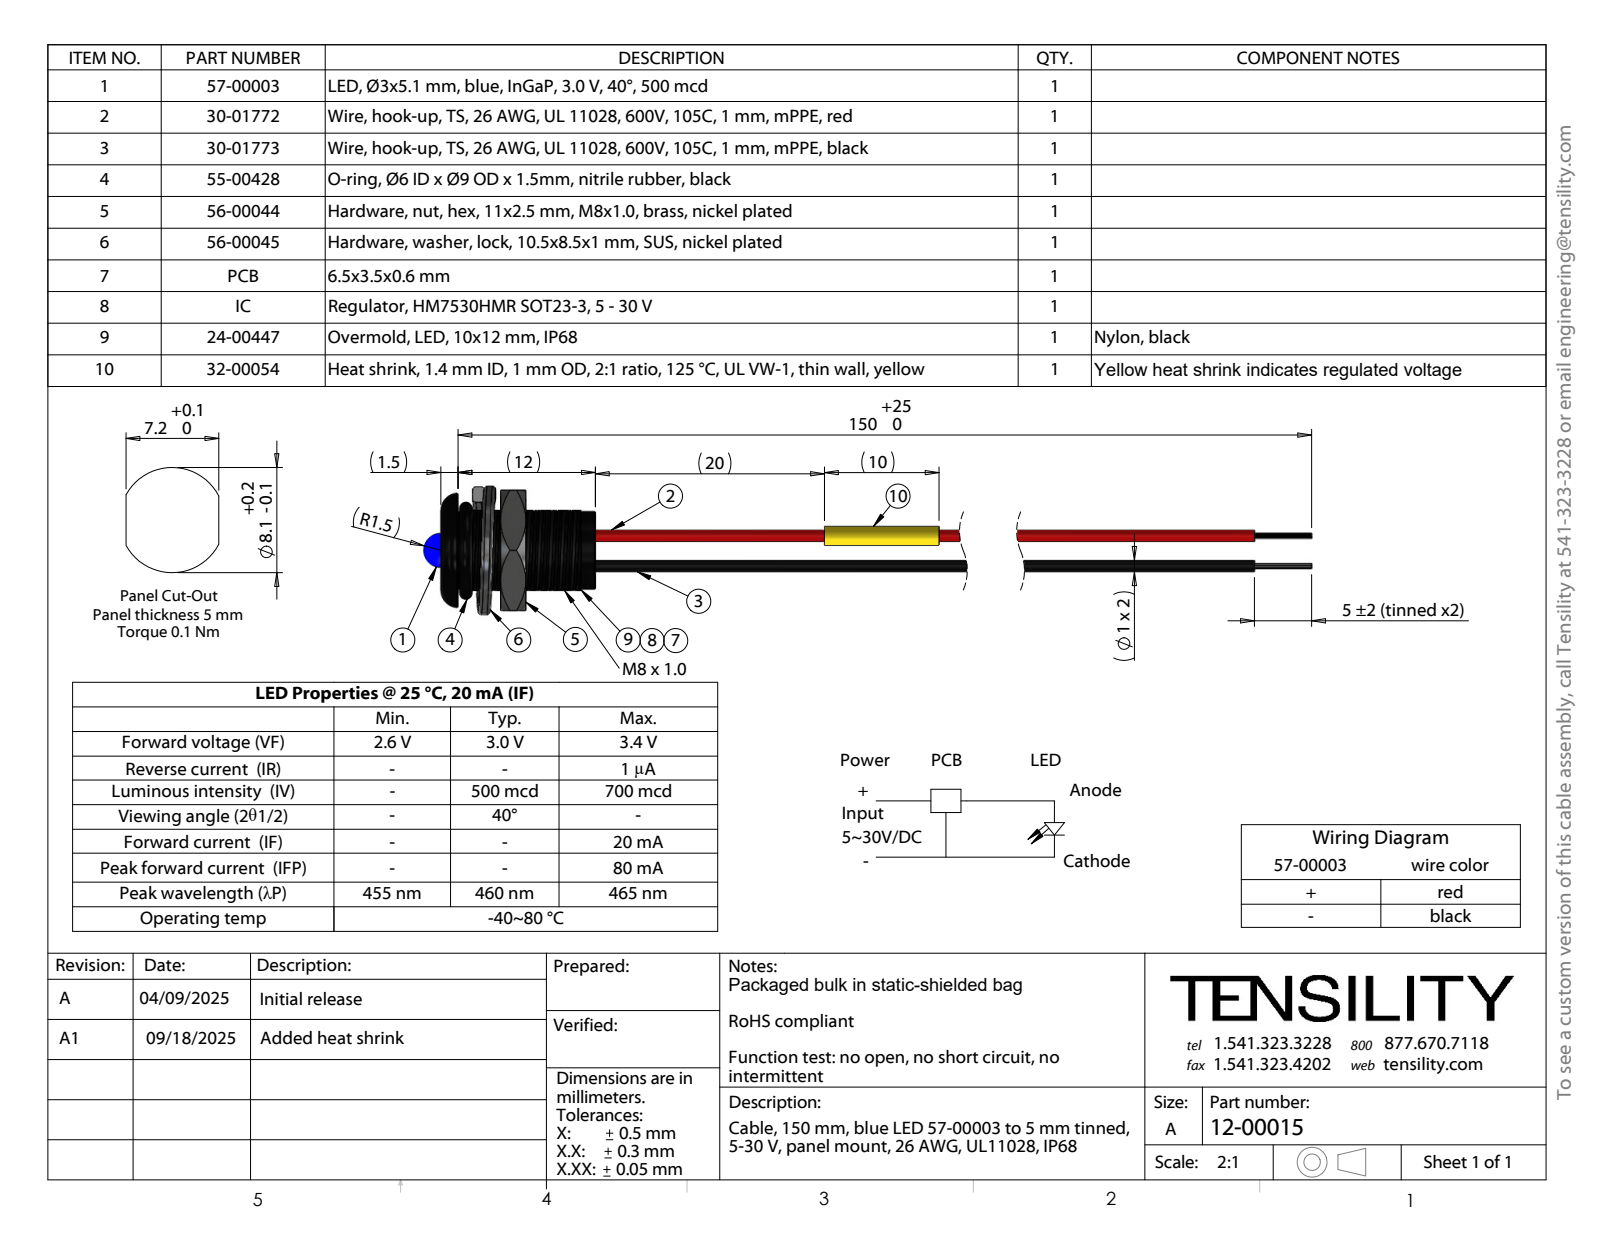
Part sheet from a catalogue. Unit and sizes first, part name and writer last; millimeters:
Units: millimetres
Overall size (bounding box): 169.99 × 12.12 × 11.21
Round holes (diameter × count): ⌀1 ×2
Round bosses / shafts (diameter × count): ⌀1 ×2, ⌀0.5 ×2, ⌀6.8 ×1, ⌀3 ×1
Partial cylindrical surfaces — rounded edges, fillets, slot ends (radius × count): R3.48 ×1, R4 ×1
Main face-to-face distances: 1.5, 13.5, 12, 10.5, 5.21, 3.71, 8.29, 7.41, 5.91, 2.2
Hole centre spacings: 0.36, 0.38, 0.33, 2.48, 2.52, 2.43, 2.44, 2.56
Volume: 1 005 mm³ · Surface area: 5 908 mm²
Bodies: 57 solids, 555 faces (186 planar, 246 cylindrical, 123 other)
Part name (STEP PRODUCT): 56-00045_Split washer; 12-00015; 30-01773_stripped and tinned; 55-00428 (+4 more)
STEP written by: SolidWorks 2021 (CONFIG_CONTROL_DESIGN)
